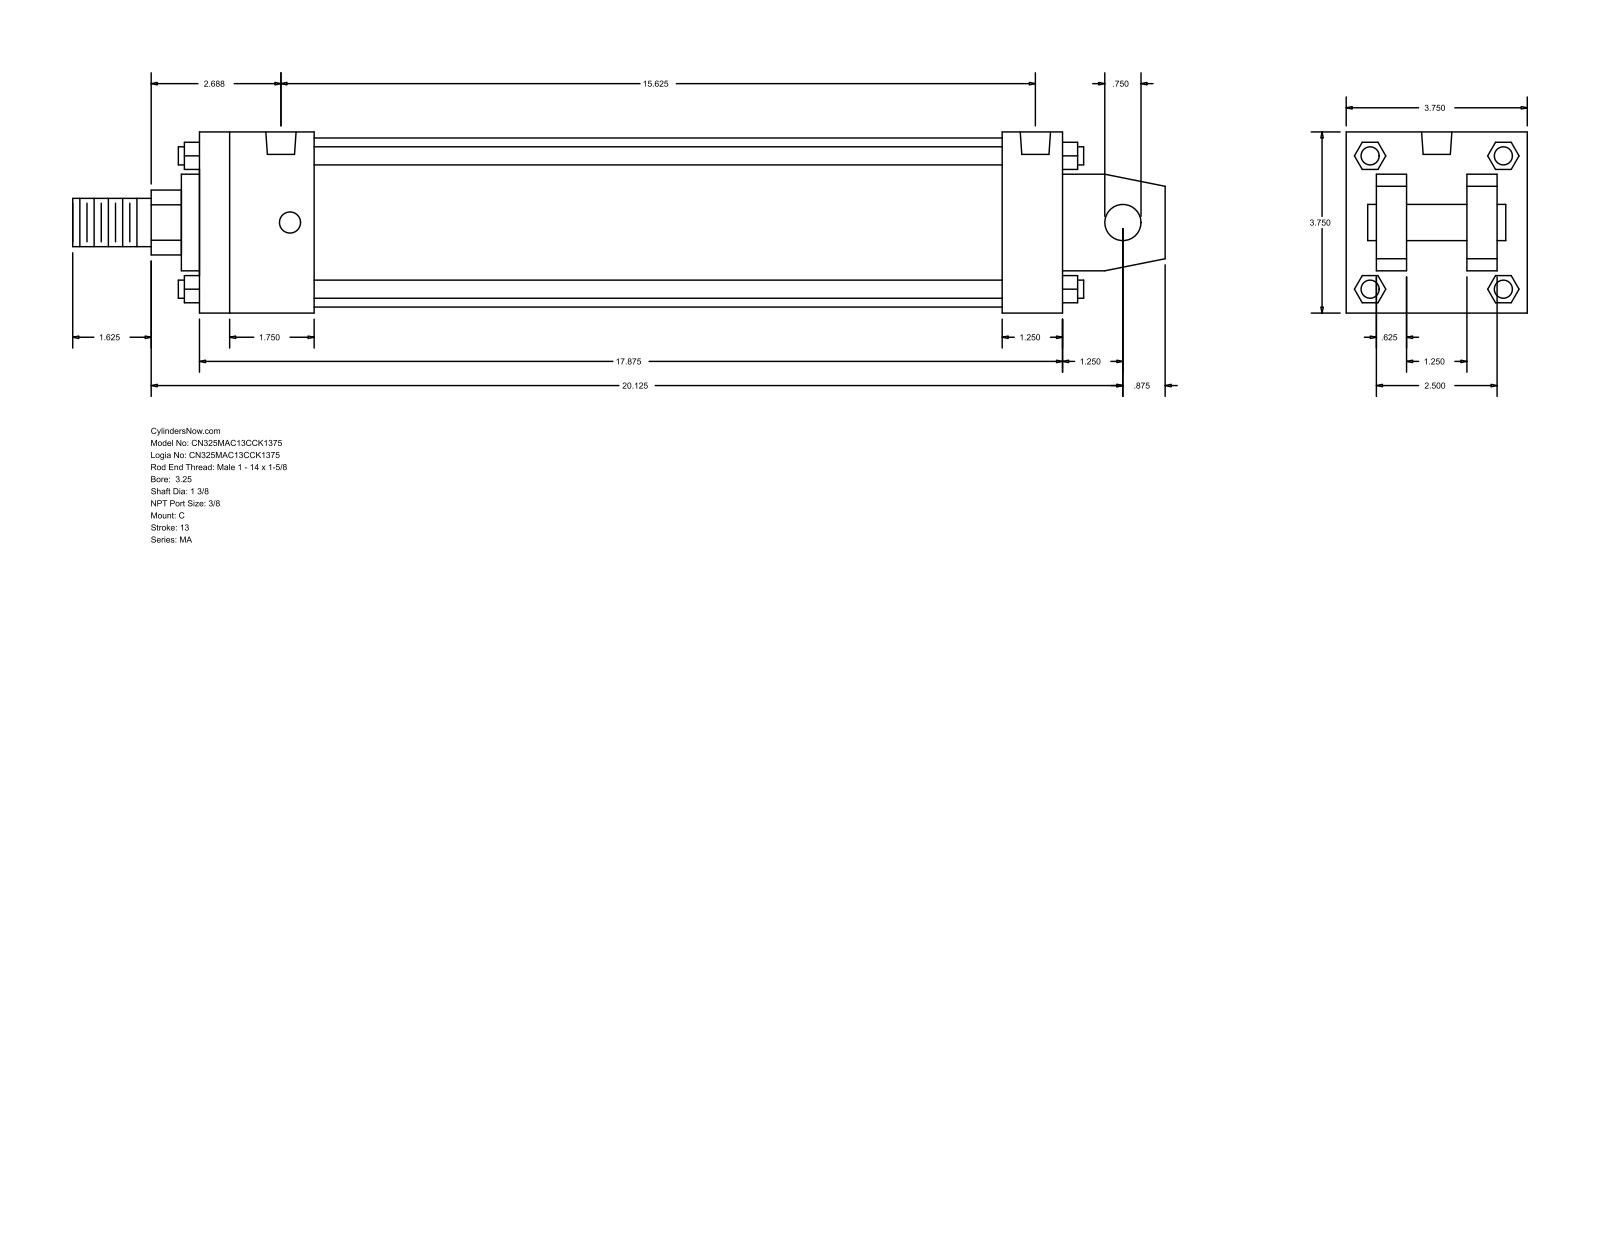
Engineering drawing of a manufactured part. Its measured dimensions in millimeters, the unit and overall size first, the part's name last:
Units: millimetres
Overall size (bounding box): 574.67 × 95.25 × 95.25
Round holes (diameter × count): ⌀11.11 ×4, ⌀15.93 ×2
Round bosses / shafts (diameter × count): ⌀9.53 ×4, ⌀88.9 ×1, ⌀50.8 ×1, ⌀34.92 ×1, ⌀25.4 ×1, ⌀19.05 ×1
Partial cylindrical surfaces — rounded edges, fillets, slot ends (radius × count): R17.06 ×1
Main face-to-face distances: 95.24, 15.87, 63.5, 454.03, 31.74, 79.37, 47.63, 422.28, 31.75, 60.32
Hole centre spacings: 387.35, 4.76, 4.77, 392.11, 392.12, 396.88
Bodies: 0 solids, 139 faces (108 planar, 31 cylindrical, 0 other)
Part name (STEP PRODUCT): MA_C__0325_1.375
STEP written by: GSSL Pune (CONFIG_CONTROL_DESIGN)
